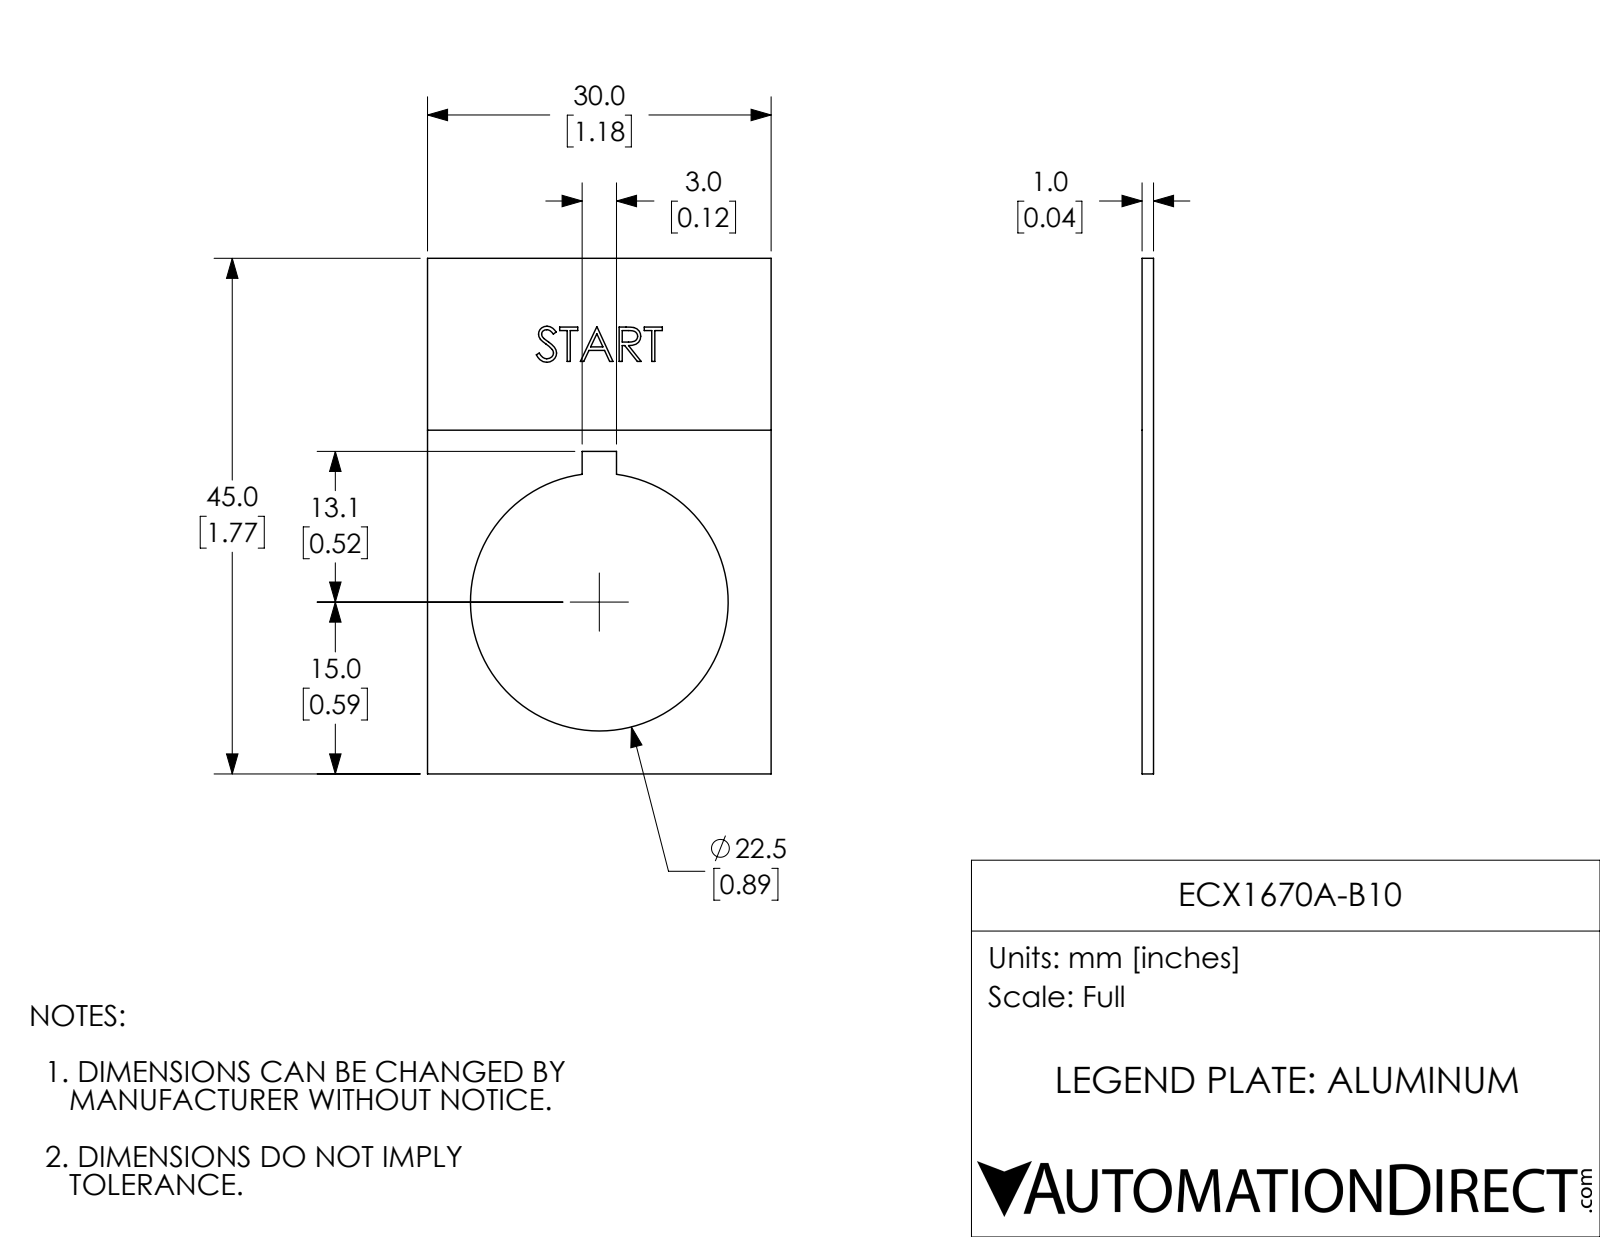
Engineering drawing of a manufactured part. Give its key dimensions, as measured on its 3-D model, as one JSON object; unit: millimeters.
{"part_name": "ECX1670A-B10", "step_written_by": "SolidWorks 2017 (AUTOMOTIVE_DESIGN)", "units": "millimeters", "bodies": {"solids": 1, "faces": 80, "planar": 57, "cylindrical": 3, "other": 20}, "overall_size": [45, 30, 1], "volume_mm3": 950, "surface_area_mm2": 2119, "round_holes": [[22.5, 1]], "face_to_face_distances": [1, 30, 45, 1, 13.5, 16.5, 28.1, 16.8, 3, 7.4]}
